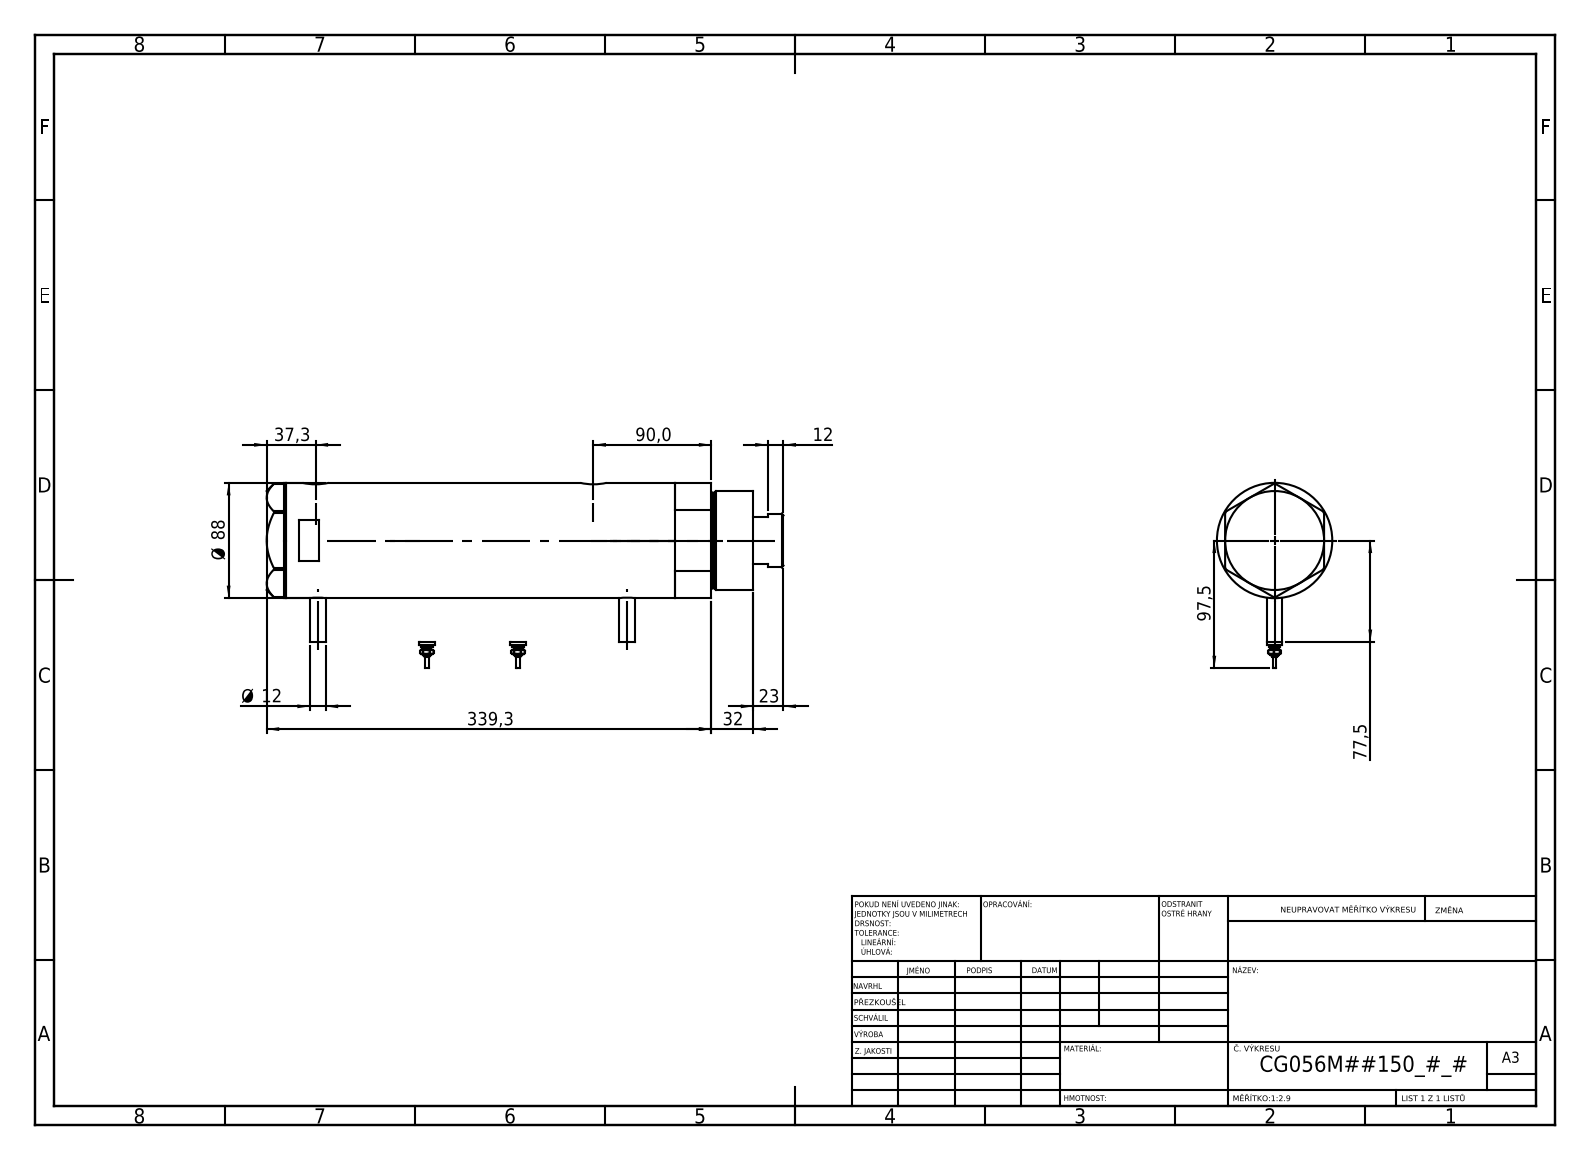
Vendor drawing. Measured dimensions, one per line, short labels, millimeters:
name: V270CG_BACK; V270CG_FRONT; V270CG_VC; Switch (+1 more)
written by: SolidWorks 2019 (CONFIG_CONTROL_DESIGN)
unit: mm
bodies: 6 solids, 213 faces (80 planar, 69 cylindrical, 64 other)
size: 394.3 × 141.5 × 88
volume: 2 042 000 mm³; area: 283 023 mm²
holes: 2× ⌀12.5, 2× ⌀13.16, 2× ⌀20, 1× ⌀14.5, 1× ⌀42, 1× ⌀43.5, 1× ⌀56, 1× ⌀60, 1× ⌀80
bosses: 4× ⌀12, 2× ⌀9, 2× ⌀7, 2× ⌀4.5, 2× ⌀2.5, 1× ⌀88, 1× ⌀75, 1× ⌀73
face distances: 234.4, 26, 208.4, 15, 41, 249.4, 356.3, 371.3, 330.3, 121.9
hole spacings: 1.7, 25.8, 210.3, 212, 236.1, 237.8
